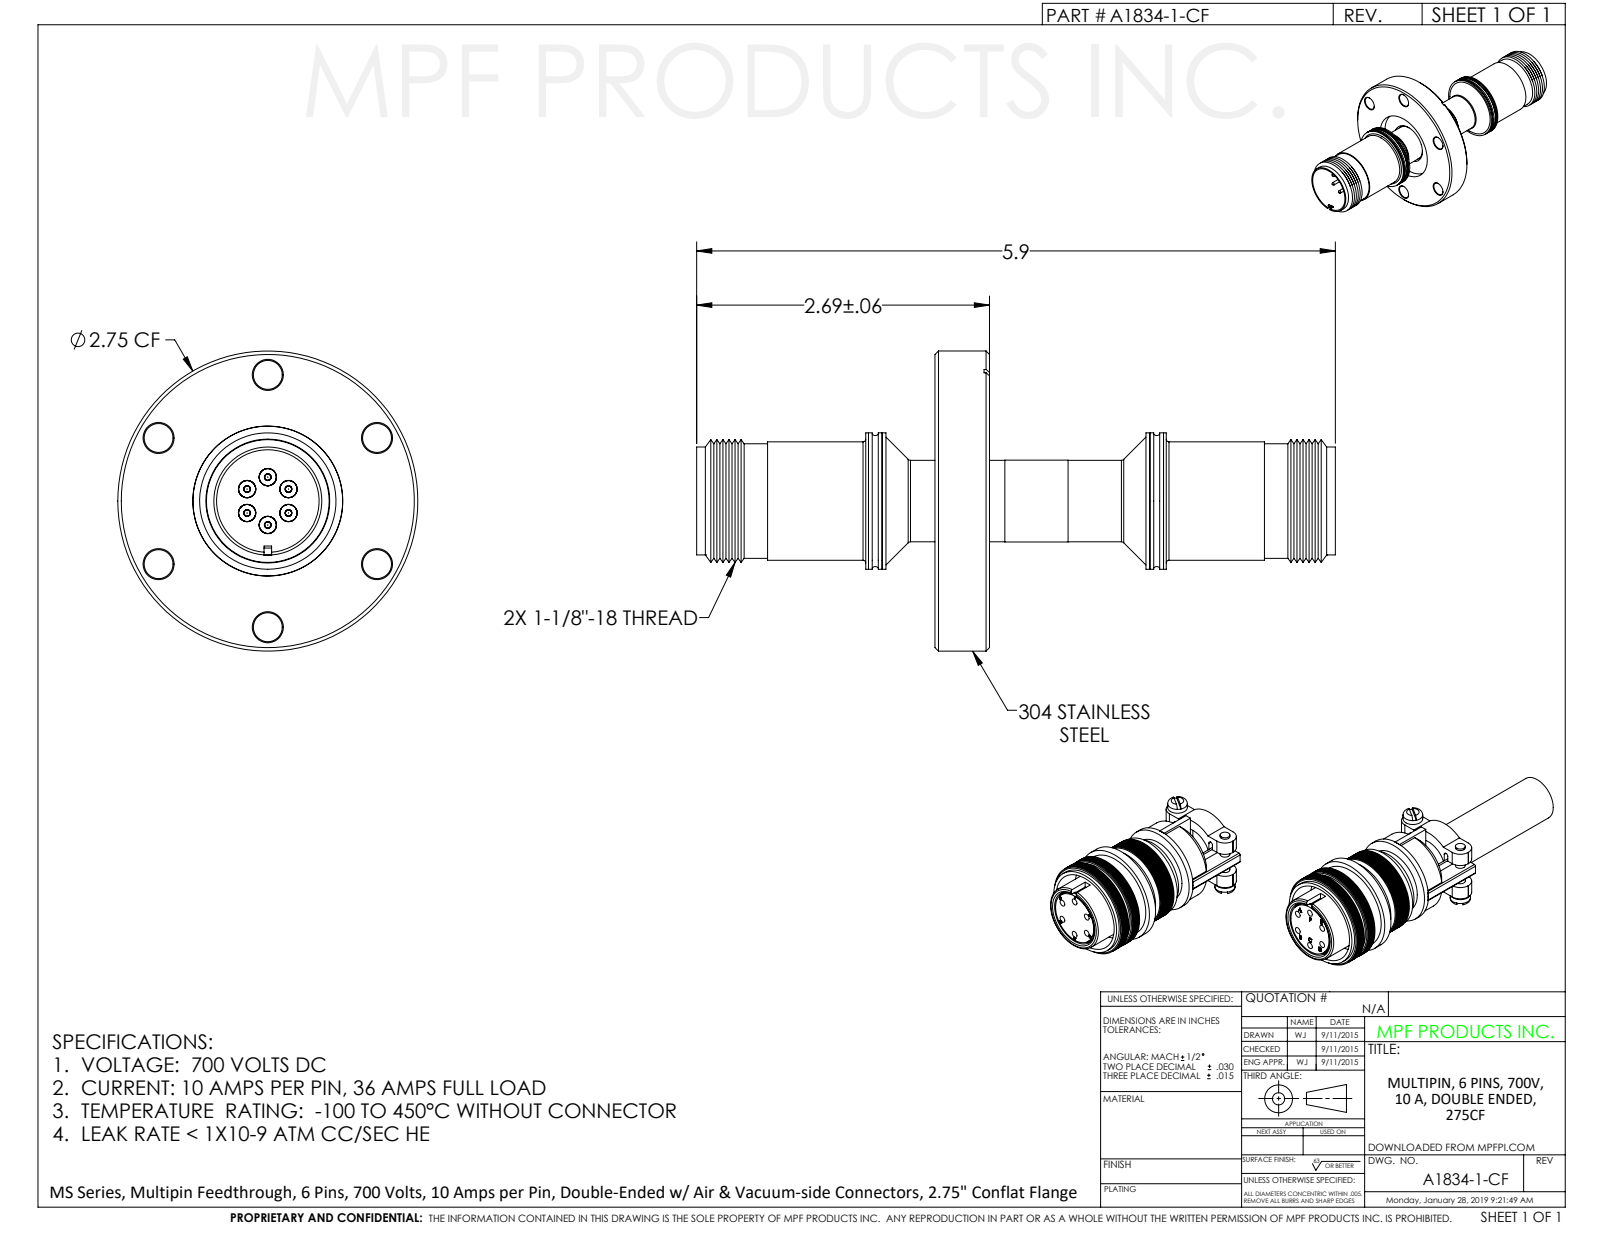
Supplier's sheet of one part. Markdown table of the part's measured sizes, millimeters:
| quantity | value |
| --- | --- |
| part name | A1834-1-CF |
| STEP written by | SolidWorks 2012 (CONFIG_CONTROL_DESIGN) |
| units | millimeters |
| bodies | 1 solid, 490 faces (111 planar, 243 cylindrical, 136 other) |
| overall size | 148.7 × 69.9 × 69.9 |
| volume | 58 680 mm³ |
| surface area | 48 500 mm² |
| round holes (diameter × count) | 4 × 6, 6.7 × 4, 6.7 × 2, 15.9 × 1, 17.1 × 1, 17.3 × 1, 19.1 × 1, 23.9 × 1, 24.4 × 1, 24.6 × 1, 26.3 × 1, 33.1 × 1 |
| round bosses / shafts (diameter × count) | 4.7 × 6, 4.4 × 6, 1.4 × 6, 4.4 × 5, 69.9 × 1, 31.8 × 1, 27.6 × 1, 26.7 × 1 |
| partial cylindrical surfaces (radius × count) | 42 × 2 |
| main face-to-face distances | 12.7, 1.3, 89.3, 9.2, 3.5, 2.8, 6.4, 9.9, 1.5, 1.3 |
| hole center spacings | 5.6, 24.7, 29.4, 34.3, 29.9, 9.6, 29.9, 50.9 |
